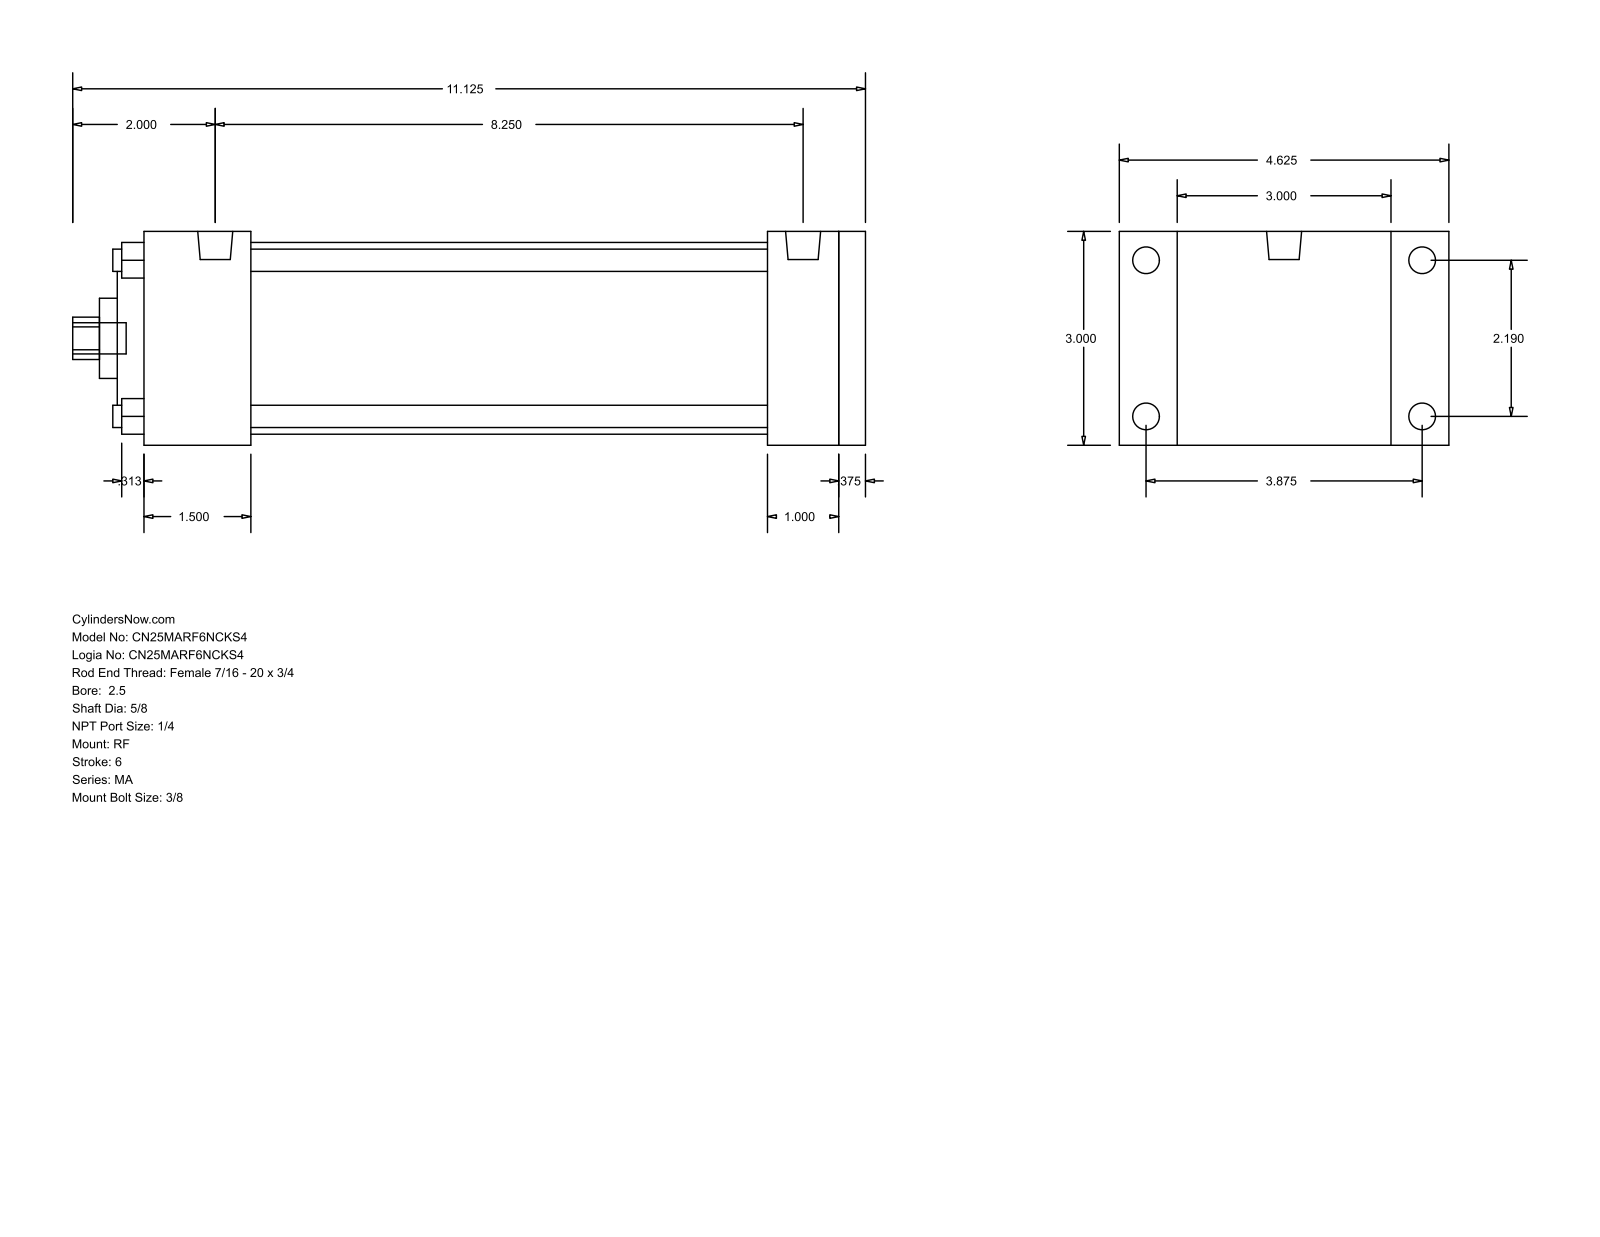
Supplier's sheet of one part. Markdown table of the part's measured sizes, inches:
| quantity | value |
| --- | --- |
| part name | MA_RF__0250_0.625 |
| STEP written by | GSSL Pune (CONFIG_CONTROL_DESIGN) |
| units | inches |
| bodies | 0 solids, 94 faces (65 planar, 29 cylindrical, 0 other) |
| overall size | 11.125 × 4.625 × 3 |
| round holes (diameter × count) | 0.313 × 4, 0.625 × 1, 1.125 × 1, 2 × 1, 2.69 × 1 |
| round bosses / shafts (diameter × count) | 0.375 × 4, 0.313 × 4, 0.492 × 2, 0.437 × 1 |
| partial cylindrical surfaces (radius × count) | 0.297 × 1 |
| main face-to-face distances | 3, 10.125, 0.375, 9.75, 1, 1.5, 8.75, 7.25, 8.25, 8.625 |
| hole center spacings | 1.548, 2.19, 3.097 |
